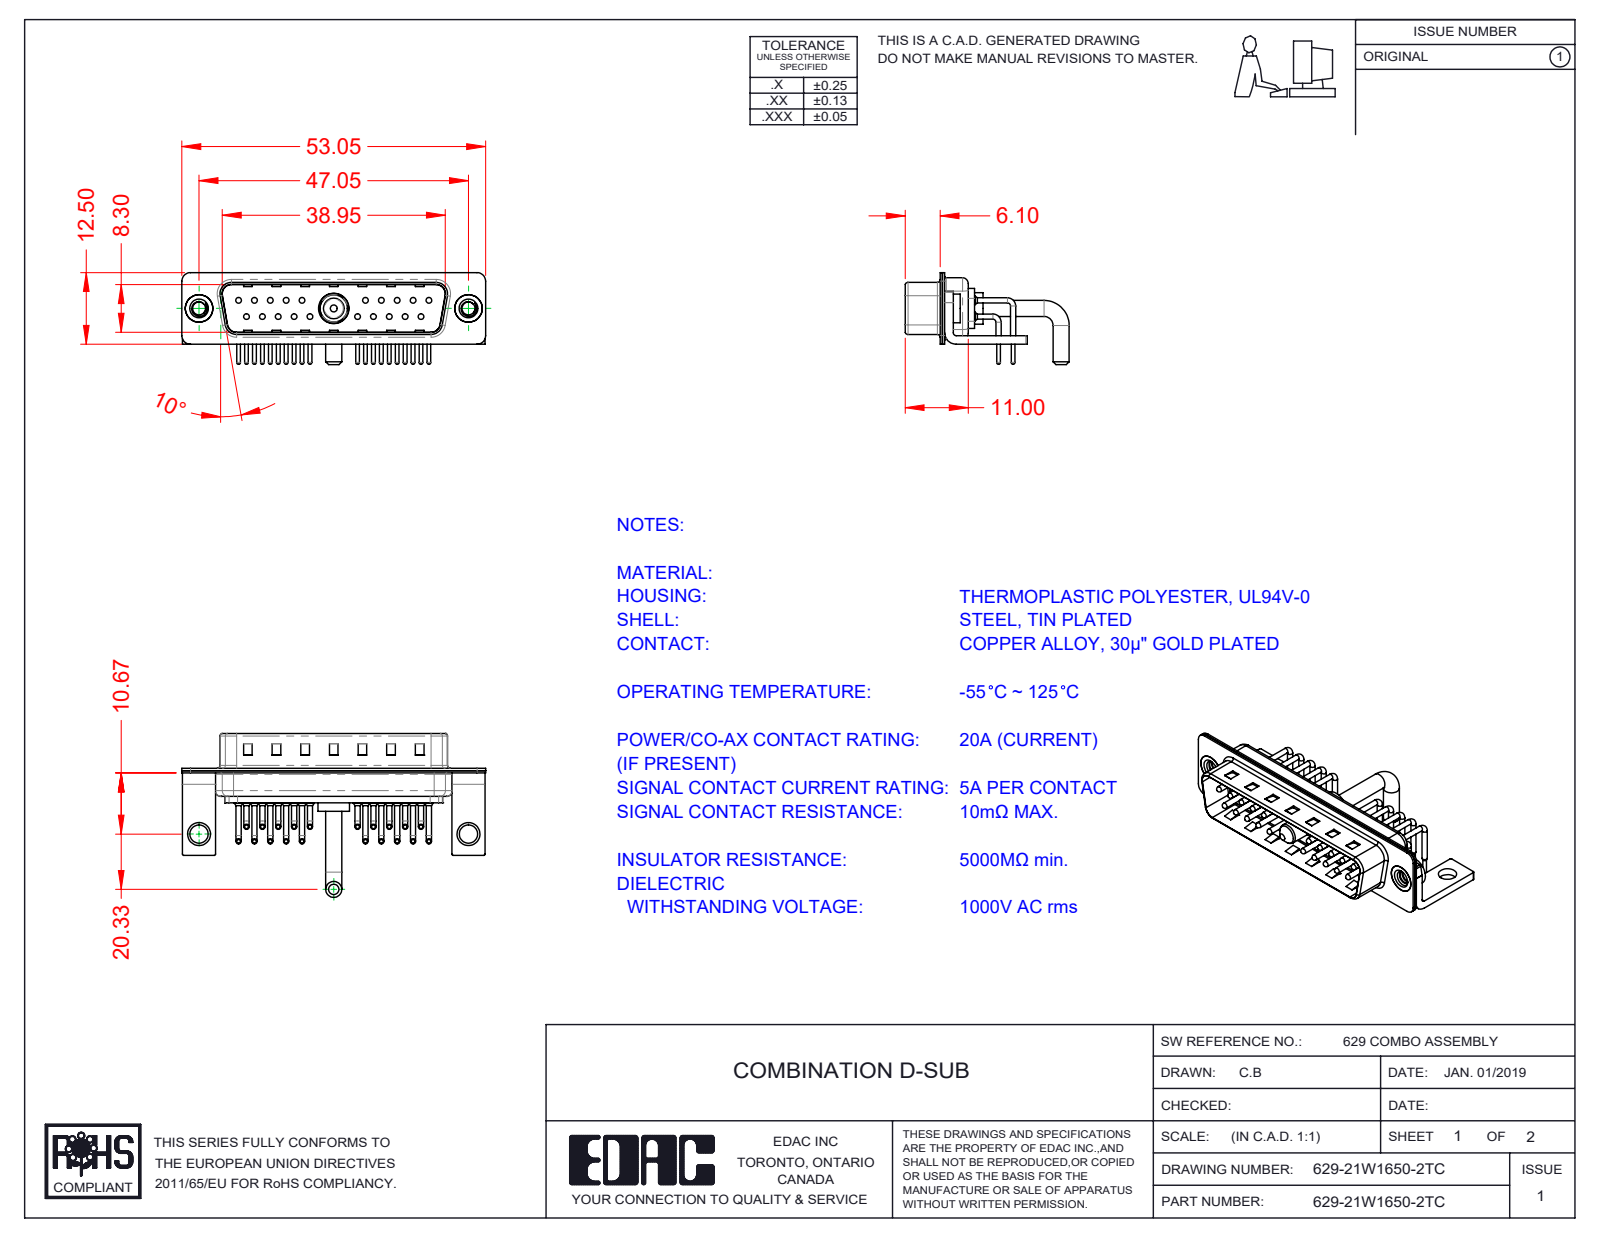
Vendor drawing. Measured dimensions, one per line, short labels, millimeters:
name: 629Combo Contact Row 2; 629Combo Stabilizer Bracket; 629Combo Threaded Rivet_2; 629Combo Shell Rear_25 Contacts (+5 more)
written by: SolidWorks 2020 (CONFIG_CONTROL_DESIGN)
unit: mm
bodies: 29 solids, 2667 faces (1481 planar, 902 cylindrical, 284 other)
size: 53.05 × 28.63 × 16.05
volume: 3 373 mm³; area: 8 300 mm²
holes: 20× ⌀0.75, 20× ⌀1.6, 20× ⌀2, 2× ⌀2.26, 2× ⌀3.2, 2× ⌀4, 2× ⌀4.8, 1× ⌀4.85, 1× ⌀5.3
bosses: 40× ⌀0.9, 20× ⌀1.5, 20× ⌀1, 20× ⌀0.65, 2× ⌀5, 2× ⌀4.9, 2× ⌀2.8, 1× ⌀5.5
rounds: 20× R1.01, 16× R0.25, 16× R1.5, 13× R2, 9× R0.5, 8× R1.6, 4× R0.6, 4× R0.65
face distances: 0.4, 0.8, 9.5, 1.5, 9.1, 8.7, 9.9, 0.6, 1.2, 2.1
hole spacings: 3.16, 2.77, 5.54, 8.31, 5.04, 19.39, 20.97, 22.16
